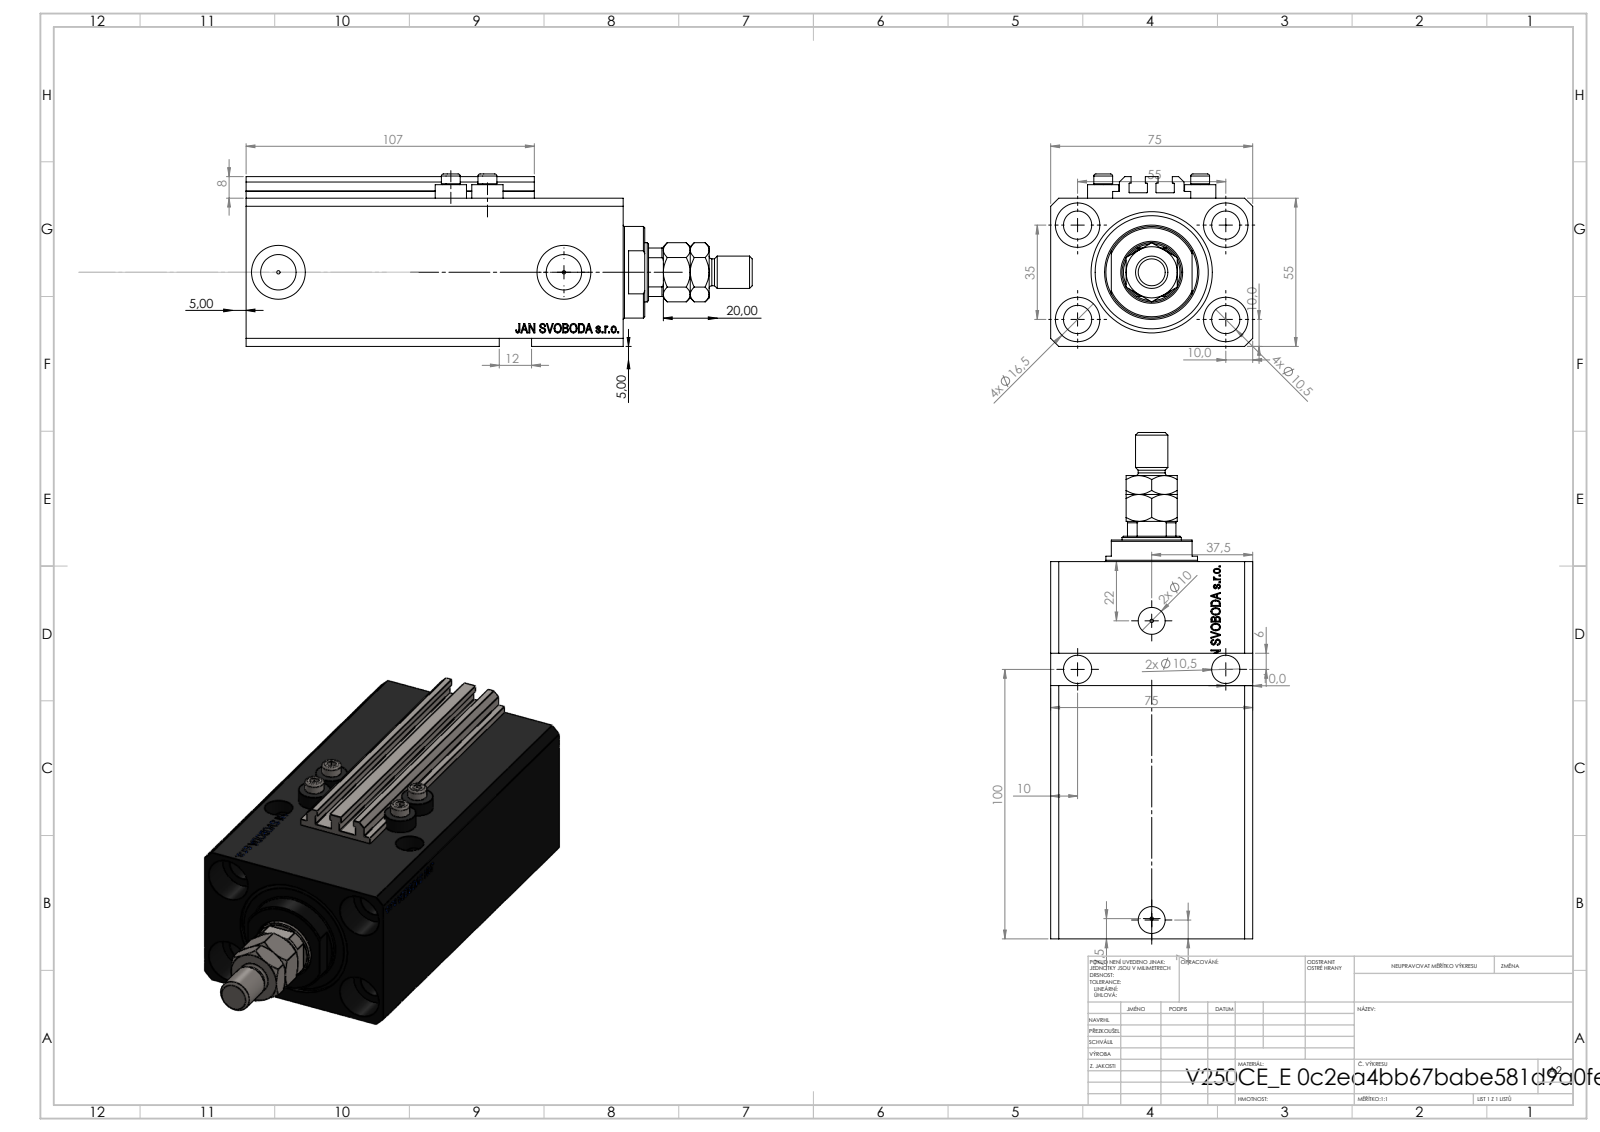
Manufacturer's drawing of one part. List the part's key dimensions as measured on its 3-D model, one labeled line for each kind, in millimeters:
Part name (STEP PRODUCT): V250CE_VC_E; V250CE_C_VCP; ALLEN BOLT V250CE; MTA (+1 more)
STEP written by: SolidWorks 2019 (CONFIG_CONTROL_DESIGN)
Units: millimetres
Bodies: 9 solids, 1133 faces (529 planar, 150 cylindrical, 454 other)
Overall size (bounding box): 188 × 75 × 64
Volume: 492 194 mm³ · Surface area: 117 621 mm²
Round holes (diameter × count): ⌀10.5 ×9, ⌀1.25 ×4, ⌀4 ×4, ⌀16.5 ×4, ⌀10 ×2, ⌀13.16 ×2, ⌀20 ×2, ⌀22 ×1, ⌀32 ×1, ⌀45 ×1
Round bosses / shafts (diameter × count): ⌀11.6 ×4, ⌀7 ×4, ⌀34 ×1, ⌀12 ×1, ⌀10 ×1
Partial cylindrical surfaces — rounded edges, fillets, slot ends (radius × count): R0.2 ×10, R10.5 ×1
Main face-to-face distances: 55, 75, 15, 140, 125, 2.5, 9.9, 3, 57, 115.1
Hole centre spacings: 32.6, 32.87, 55, 96.98, 13.6, 14.09, 25.81, 32.58
